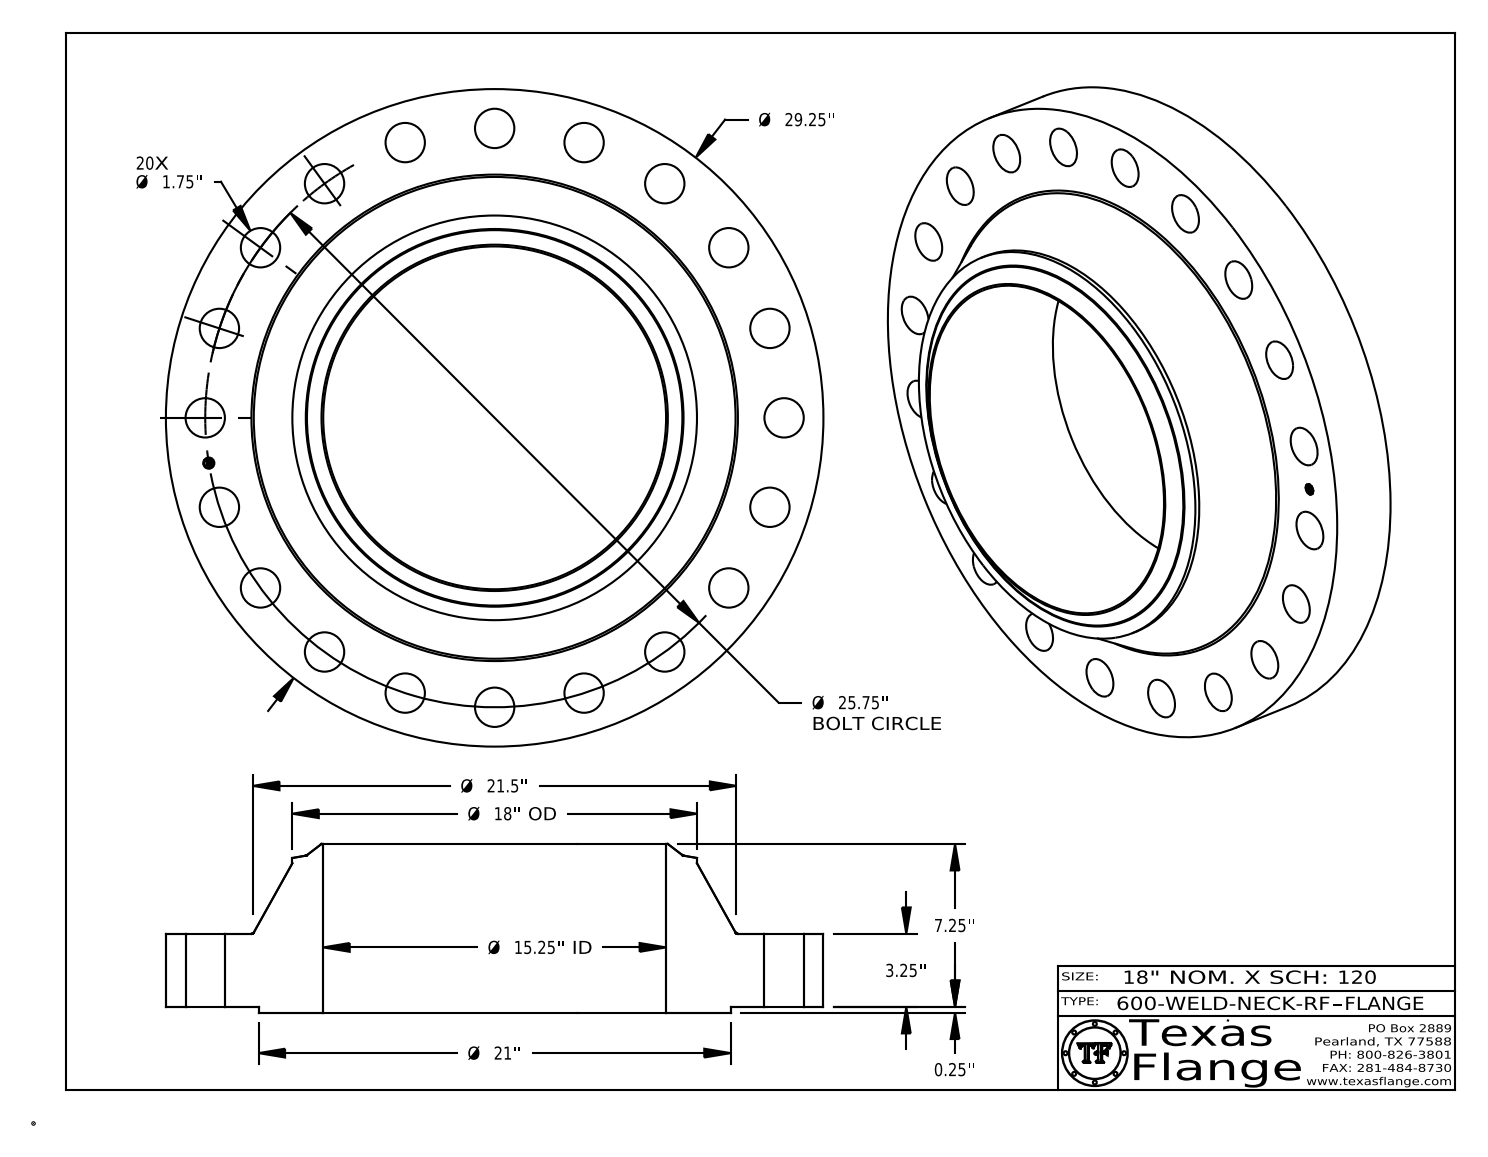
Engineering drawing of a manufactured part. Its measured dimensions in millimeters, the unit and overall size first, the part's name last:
Units: millimetres
Overall size (bounding box): 743 × 743 × 190.5
Round holes (diameter × count): ⌀44.5 ×20, ⌀12.6 ×1, ⌀387.4 ×1
Round bosses / shafts (diameter × count): ⌀0.8 ×8, ⌀743 ×1, ⌀533.4 ×1, ⌀457.2 ×1, ⌀9.9 ×1
Main face-to-face distances: 82.6, 6.4, 88.9, 190.5, 184.2, 101.6, 0.4, 88.5, 82.2, 102
Hole centre spacings: 327, 622, 646, 202.1, 297, 102.3, 384.4, 462.5
Volume: 31 120 000 mm³ · Surface area: 1 323 000 mm²
Bodies: 1 solid, 447 faces (369 planar, 68 cylindrical, 10 other)
Part name (STEP PRODUCT): 600-WELD-NECK-RF
STEP written by: CATIA V5 STEP AP214 (AUTOMOTIVE_DESIGN)
